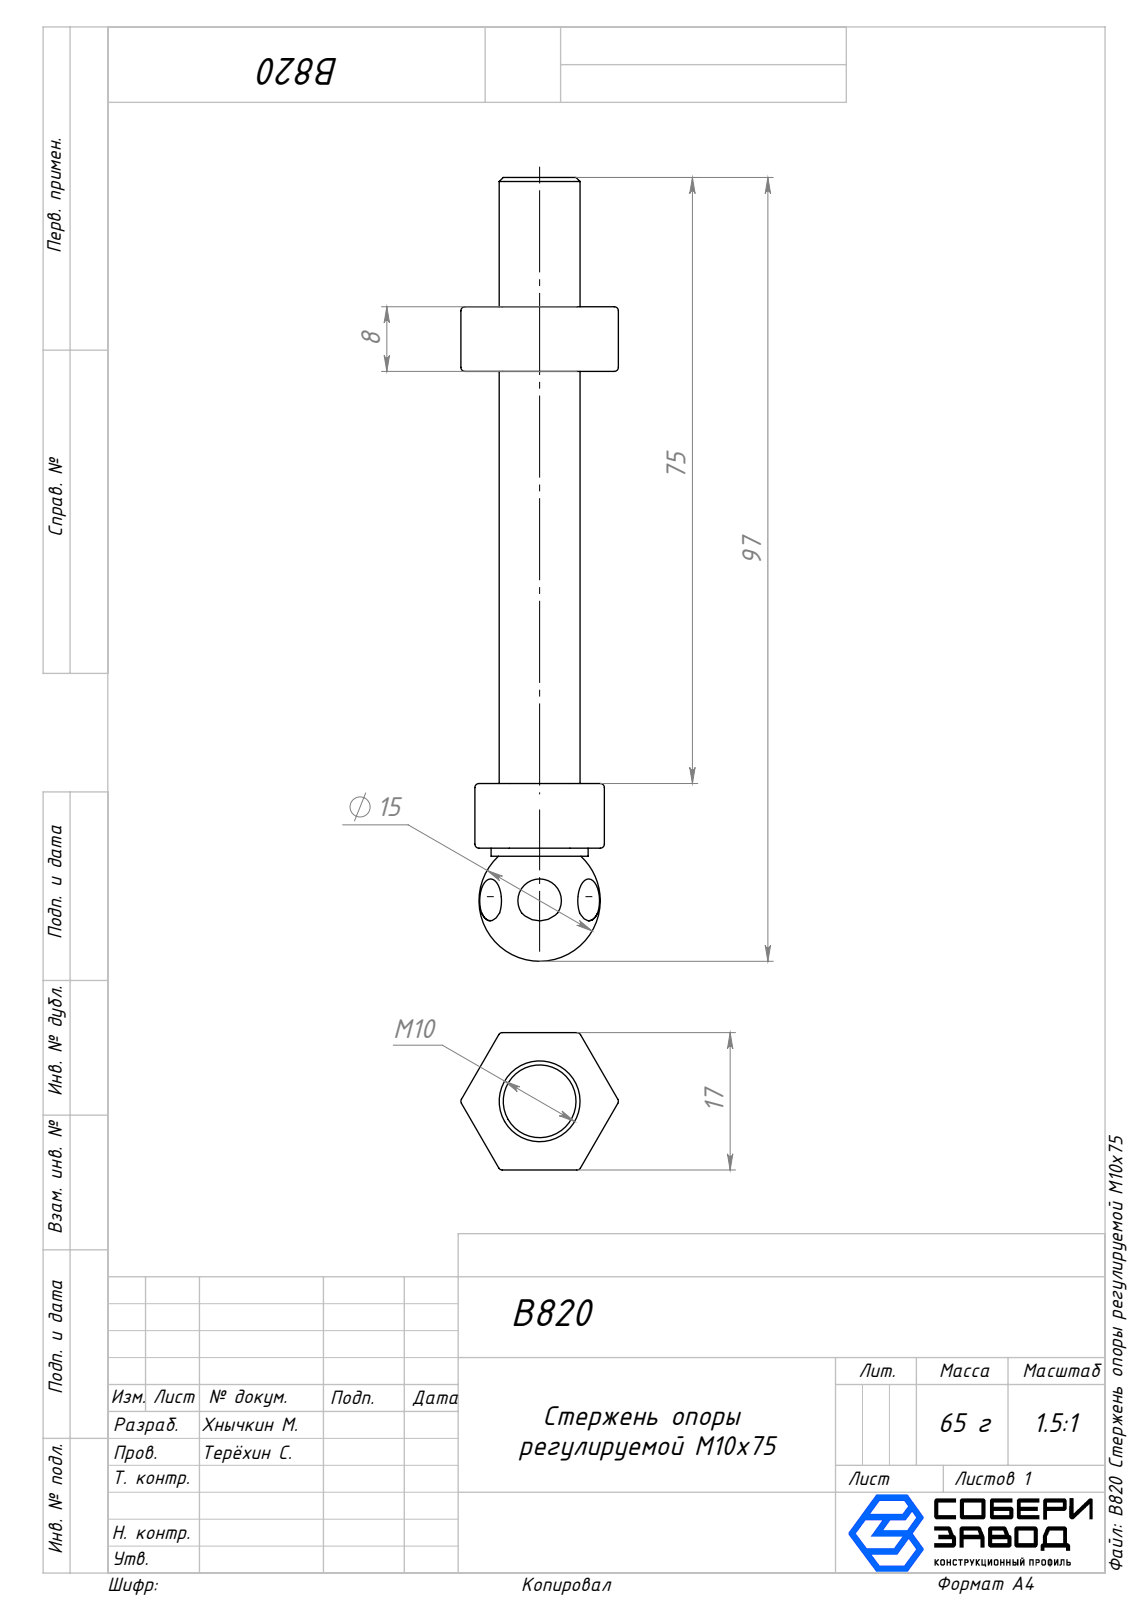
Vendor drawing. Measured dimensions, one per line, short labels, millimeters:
name: B820 Стержень опоры регулируемой М10х75; Стержень_00; Гайка_00
written by: SolidWorks 2025 (AUTOMOTIVE_DESIGN)
unit: mm
bodies: 2 solids, 104 faces (24 planar, 48 cylindrical, 32 other)
size: 97 × 19.48 × 17
volume: 10 586 mm³; area: 4 646 mm²
holes: 1× ⌀8
bosses: 1× ⌀12, 1× ⌀10
rounds: 36× R0.5, 3× R3
face distances: 1.5, 15.5, 14, 17, 8, 59, 51, 75, 24, 16
